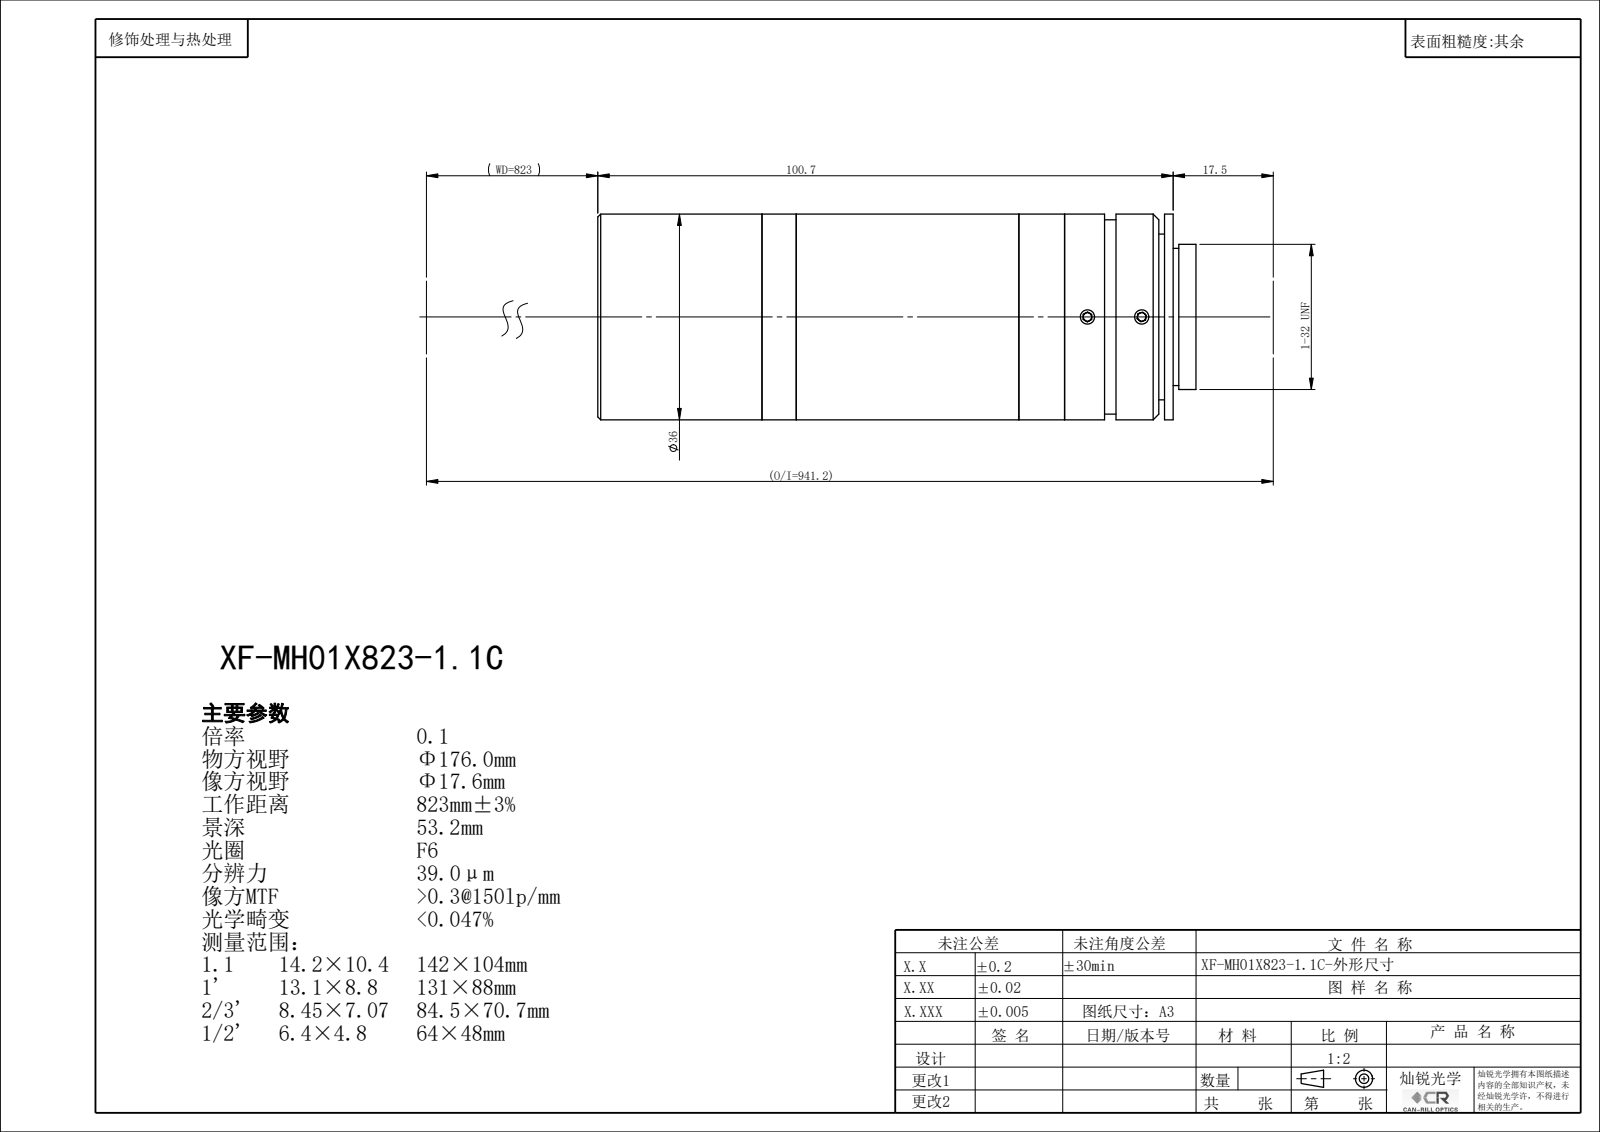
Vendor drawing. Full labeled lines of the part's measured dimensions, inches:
Part name (STEP PRODUCT): XF-MH01X823-1.1C
STEP written by: SolidWorks 2022 (CONFIG_CONTROL_DESIGN)
Units: inches
Bodies: 0 solids, 130 faces (68 planar, 46 cylindrical, 16 other)
Overall size (bounding box): 4.123 × 1.417 × 1.417
Round holes (diameter × count): ⌀0.098 ×6, ⌀0.882 ×1, ⌀0.945 ×1, ⌀1.024 ×1, ⌀1.039 ×1, ⌀1.157 ×1, ⌀1.315 ×1, ⌀1.358 ×1
Round bosses / shafts (diameter × count): ⌀1.417 ×1, ⌀1.339 ×1, ⌀1 ×1
Main face-to-face distances: 0.748, 0.551, 0.059, 0.039, 0.413, 0.689, 0.315, 1.004, 1.063, 0.236
Hole centre spacings: 0.374
